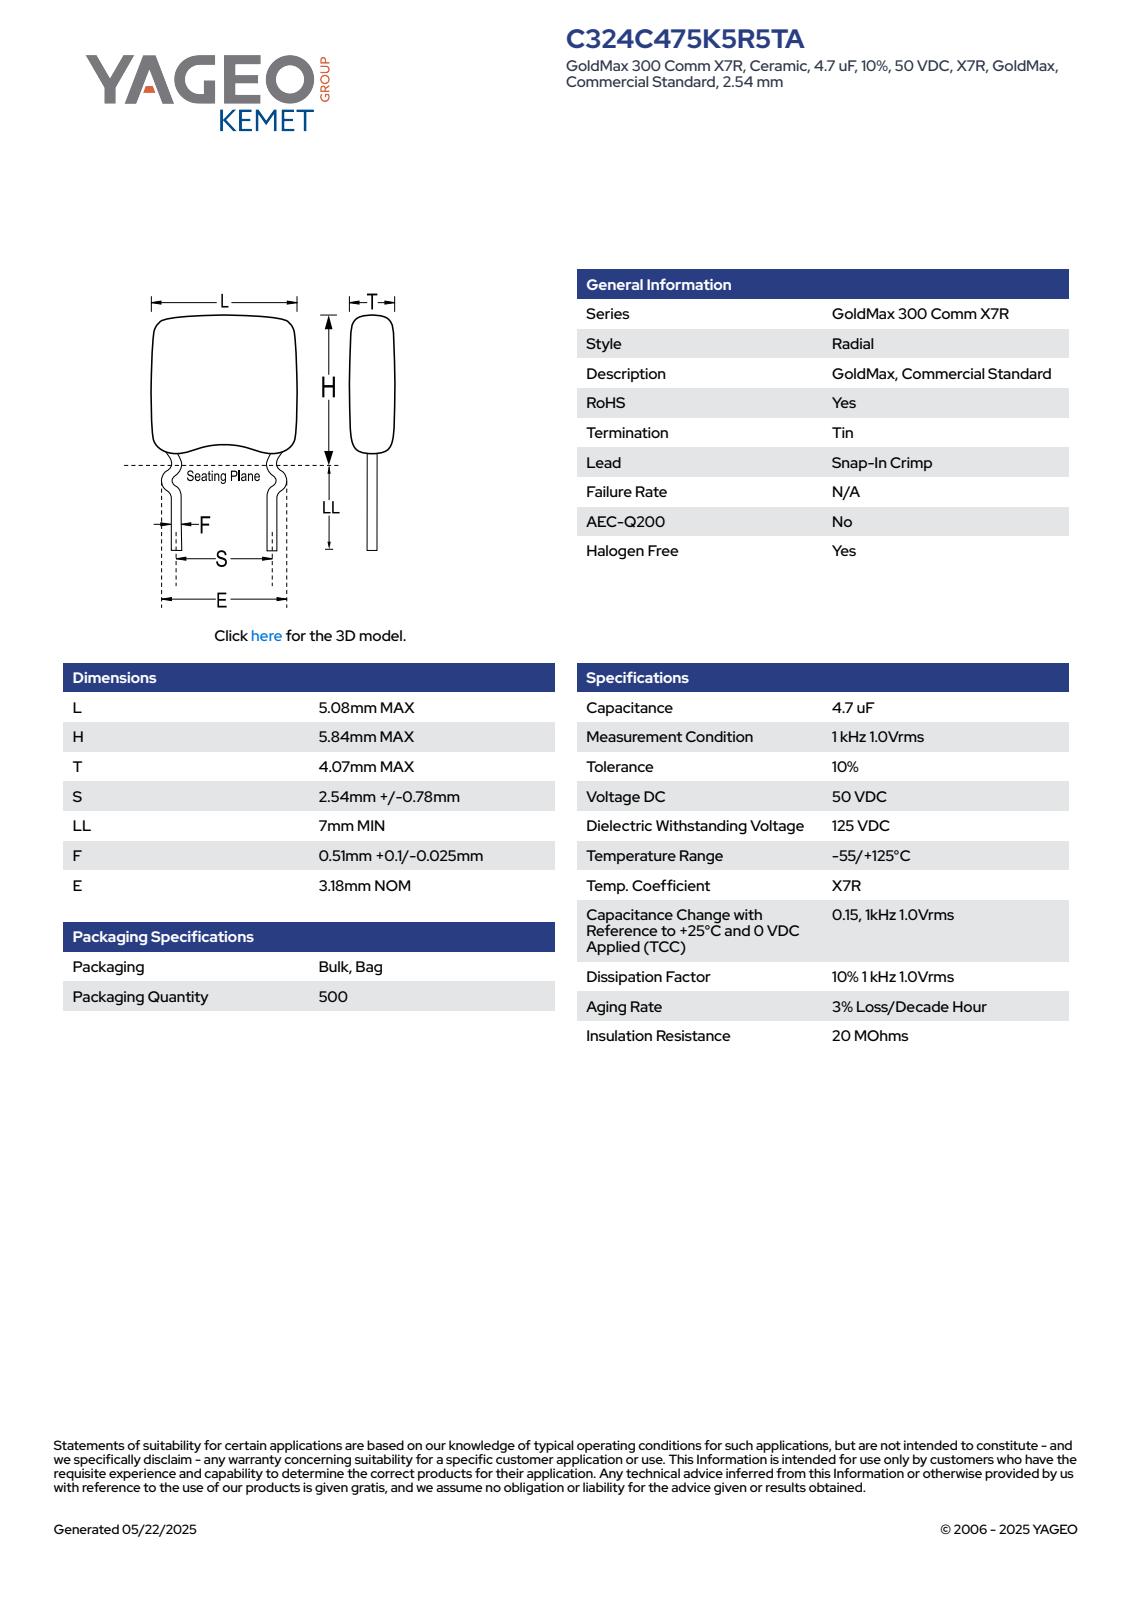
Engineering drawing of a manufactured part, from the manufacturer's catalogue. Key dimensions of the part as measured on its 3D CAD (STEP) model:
Part name (STEP PRODUCT): CCR_SICR2_5.08X5.84_L5.08H5.84T4.07S2.54LL7F0.51E3.18
STEP written by: SolidWorks 2014 (AUTOMOTIVE_DESIGN)
Units: millimetres
Bodies: 4 solids, 101 faces (65 planar, 12 cylindrical, 24 other)
Overall size (bounding box): 12.84 × 5.08 × 4.08
Volume: 92 mm³ · Surface area: 132 mm²
Partial cylindrical surfaces — rounded edges, fillets, slot ends (radius × count): R1 ×12
Main face-to-face distances: 4.07, 4.81, 5.08, 4.08, 8.03, 12.84, 10.16, 2.13, 2.68, 2.37
